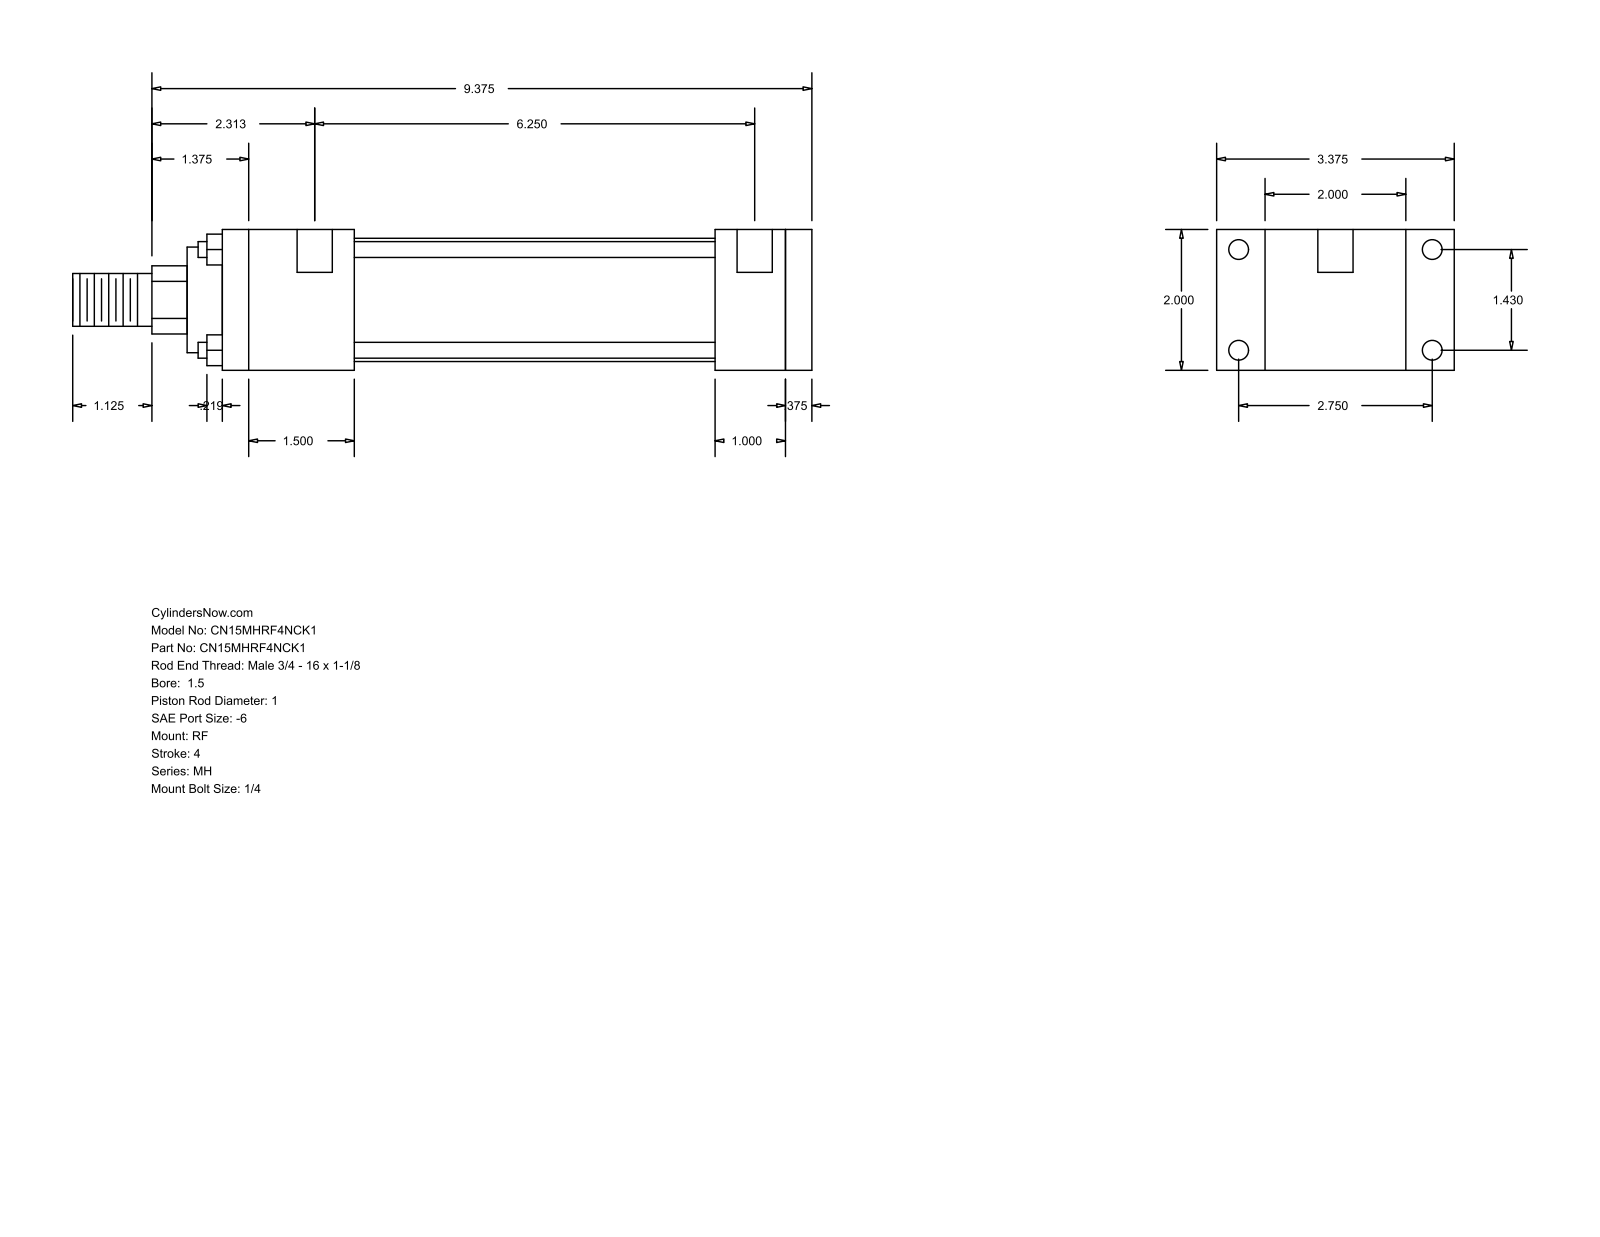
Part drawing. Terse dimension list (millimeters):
name: MH_RF__0150_1
written by: GSSL Pune (CONFIG_CONTROL_DESIGN)
unit: mm
bodies: 0 solids, 92 faces (64 planar, 28 cylindrical, 0 other)
size: 266.7 × 85.72 × 50.8
holes: 4× ⌀5.56, 4× ⌀7.14, 2× ⌀12.7
bosses: 4× ⌀5.71, 1× ⌀44.45, 1× ⌀38.1, 1× ⌀25.4, 1× ⌀19.05
rounds: 1× R12.29
face distances: 50.8, 9.52, 203.2, 25.4, 212.72, 17.46, 68.26, 177.8, 34.92, 47.63
hole spacings: 36.32, 69.84, 78.72, 161.93, 3.18, 158.75
